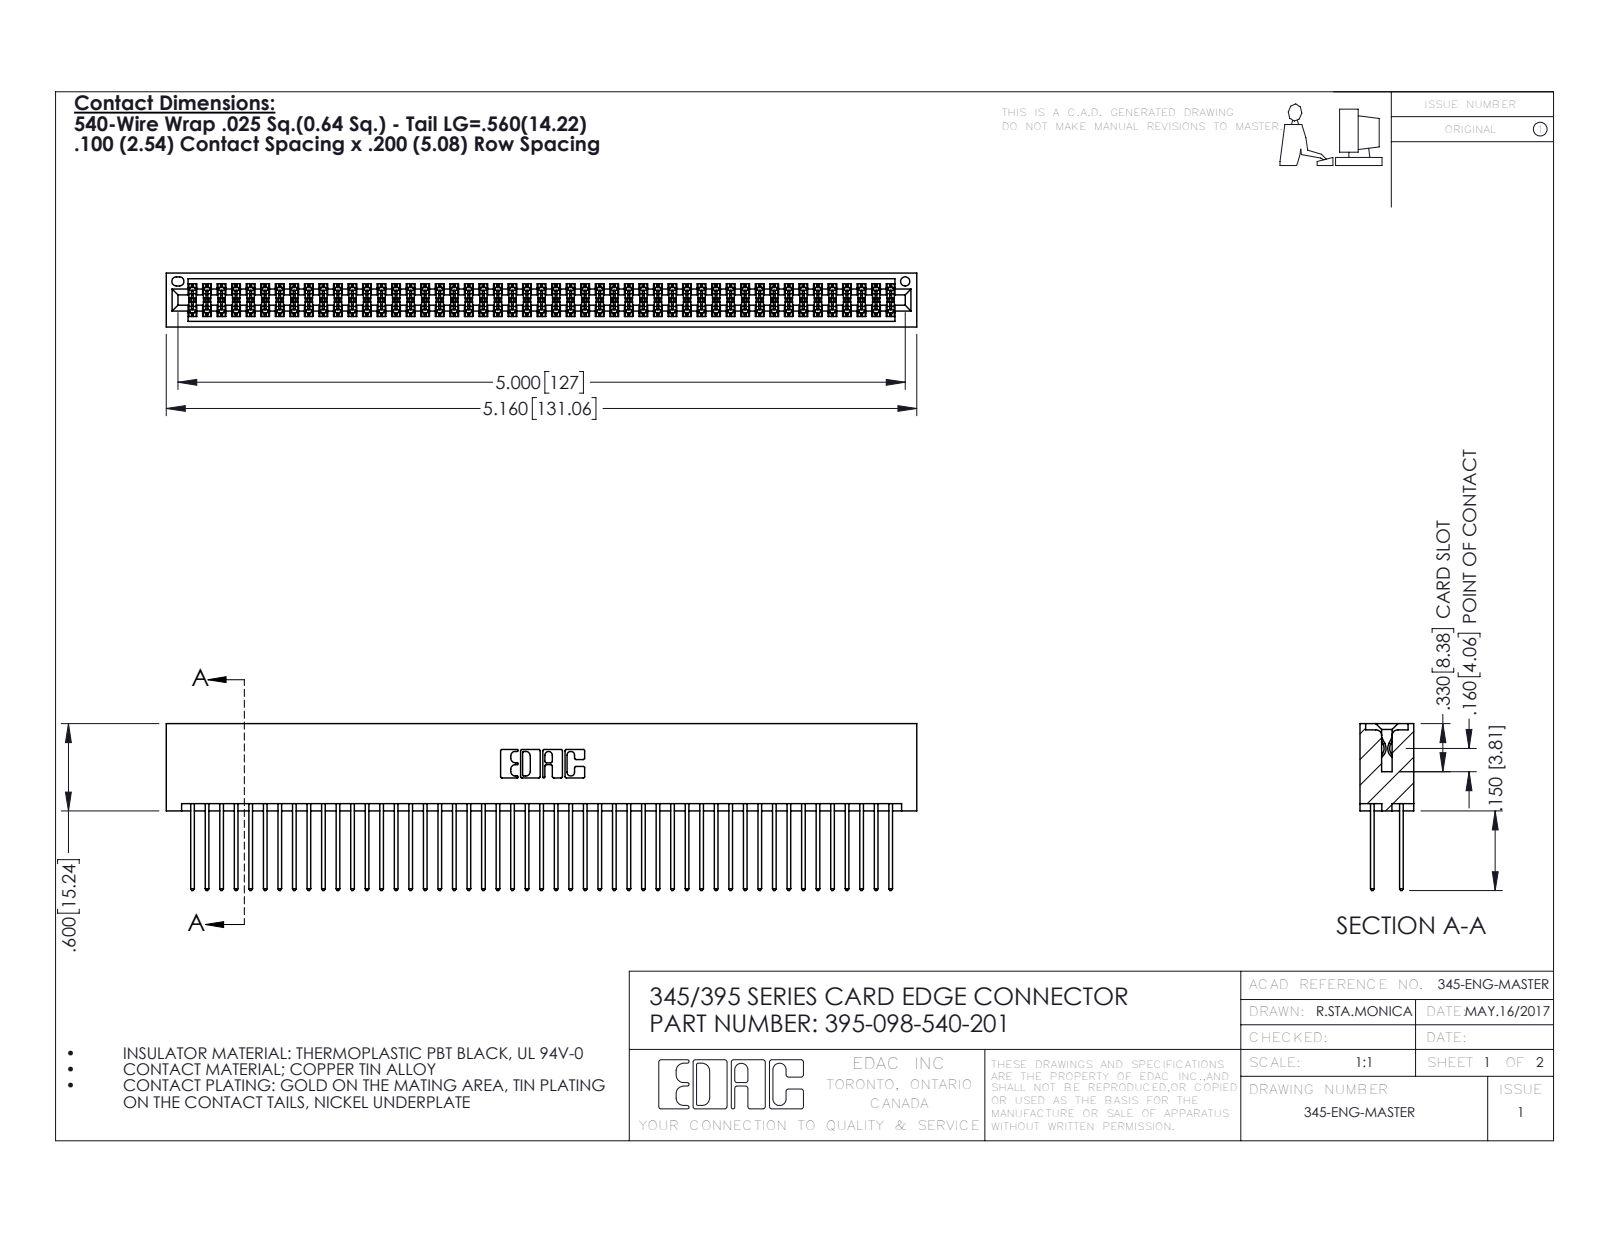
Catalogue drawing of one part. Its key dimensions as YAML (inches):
part_name: "345-292-001_345-293-140; 345 Part_No Mounting Lugs; 395-098-540-201"
step_written_by: "SolidWorks 2016 (CONFIG_CONTROL_DESIGN)"
units: inches
bodies: {solids: 99, faces: 5018, planar: 3310, cylindrical: 1708, other: 0}
overall_size: [5.16, 1.147, 0.37]
volume: 0.841
surface_area: 34.93
round_holes:
  - {diameter: 0.064, count: 1}
partial_cylinders:
  - {radius: 0.006, count: 147}
  - {radius: 0.01, count: 98}
  - {radius: 0.01, count: 22}
  - {radius: 0.007, count: 6}
  - {radius: 0.031, count: 6}
  - {radius: 0.026, count: 3}
  - {radius: 0.014, count: 2}
  - {radius: 0.019, count: 2}
face_to_face_distances: [0.298, 0.072, 0.2, 0.098, 0.272, 0.025, 0.225, 0.37, 0.175, 0.149]
